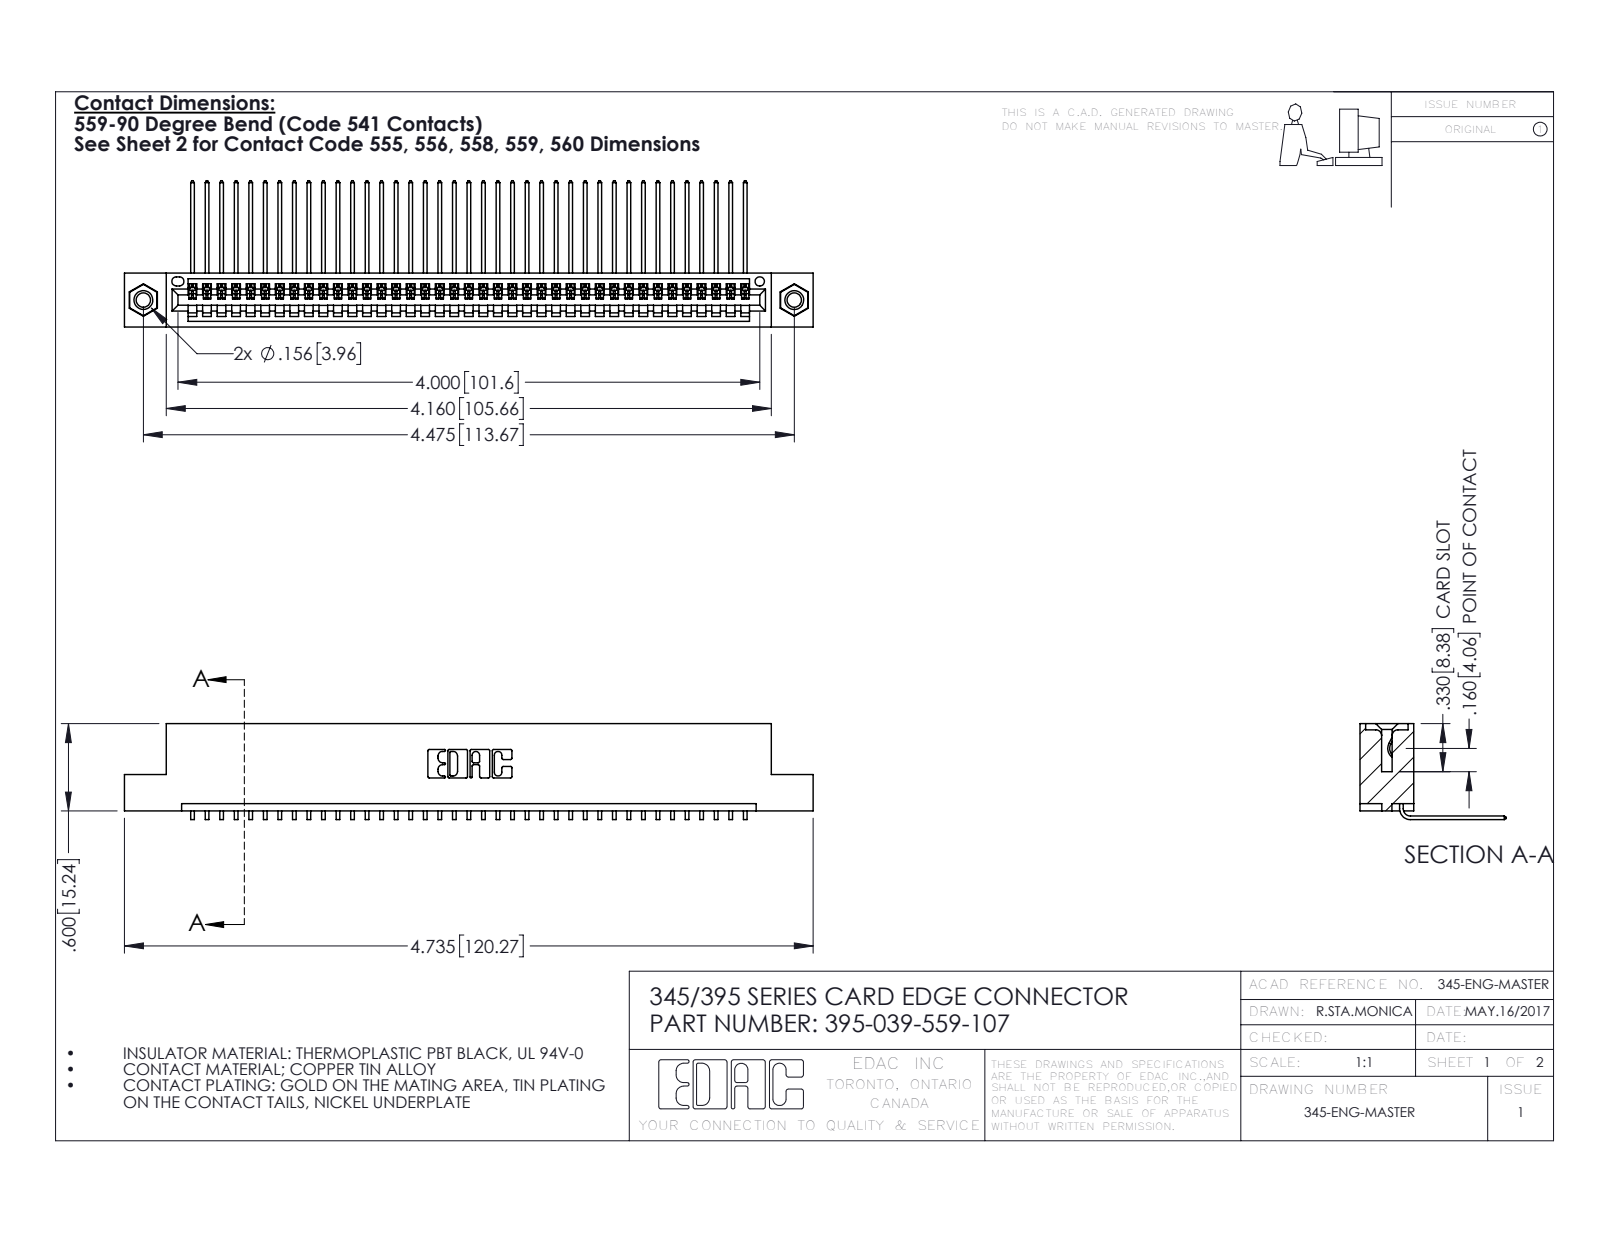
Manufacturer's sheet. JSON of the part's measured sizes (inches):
{"part_name": "345-292-001_558 559 Tail - 1; 395-039-559-107; 345 Part_Flush Mounting Lugs - 0.156 Dia-TI; 345-250-001_345-250-005-103", "step_written_by": "SolidWorks 2016 (CONFIG_CONTROL_DESIGN)", "units": "inches", "bodies": {"solids": 42, "faces": 2526, "planar": 1750, "cylindrical": 760, "other": 16}, "overall_size": [4.735, 1.005, 0.659], "volume_in3": 0.703, "surface_area_in2": 24.89, "round_holes": [[0.098, 2], [0.125, 2], [0.156, 2], [0.064, 1]], "round_bosses_or_shafts": [[0.155, 2]], "partial_cylinders_radius": [[0.006, 78], [0.01, 22], [0.007, 6], [0.031, 6], [0.026, 3], [0.031, 2], [0.04, 2], [0.014, 1]], "face_to_face_distances": [0.072, 0.298, 0.37, 0.2, 0.098, 0.272, 0.025, 0.225, 0.149, 0.072], "hole_center_spacings": [0.27, 4.239, 4.475]}
